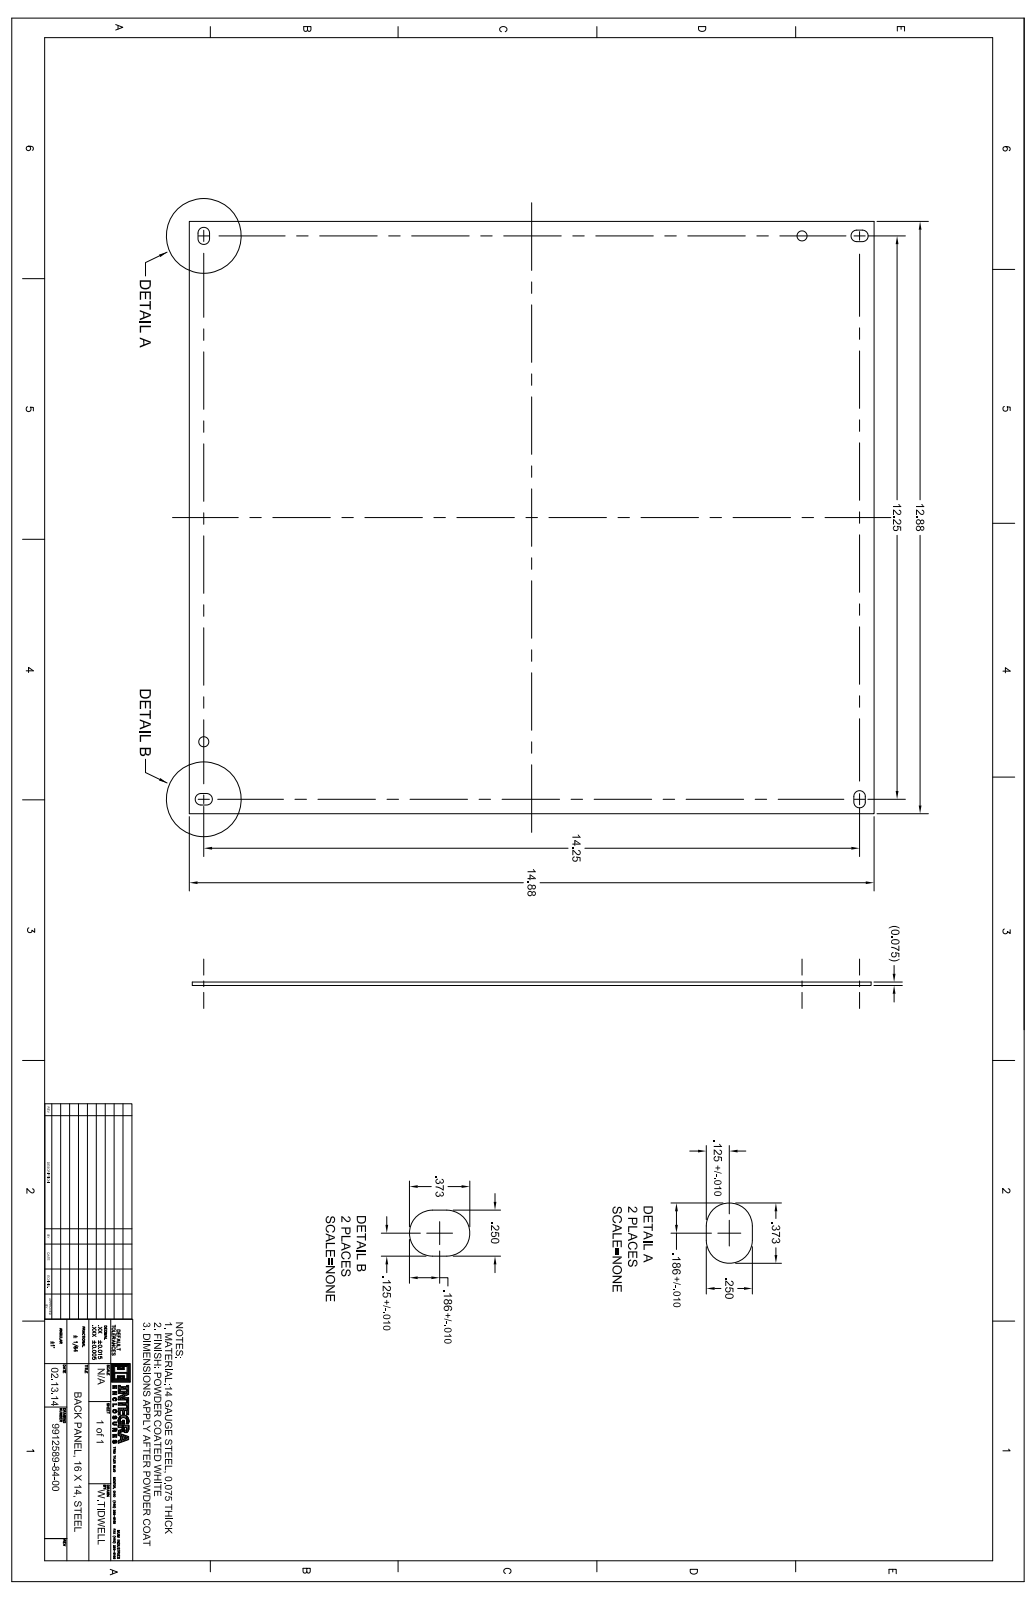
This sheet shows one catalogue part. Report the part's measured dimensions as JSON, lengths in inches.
{"part_name": "SBP-1614-P10", "step_written_by": "SolidWorks 2018 (AUTOMOTIVE_DESIGN)", "units": "inches", "bodies": {"solids": 1, "faces": 24, "planar": 14, "cylindrical": 10, "other": 0}, "overall_size": [14.88, 12.88, 0.075], "volume_in3": 14.34, "surface_area_in2": 387.1, "round_holes": [[0.219, 2]], "partial_cylinders_radius": [[0.125, 8]], "face_to_face_distances": [0.075, 12.88, 14.88, 0.19, 0.44, 0.25, 12.44, 12.69, 12.25, 14.44], "hole_center_spacings": [17.03]}
